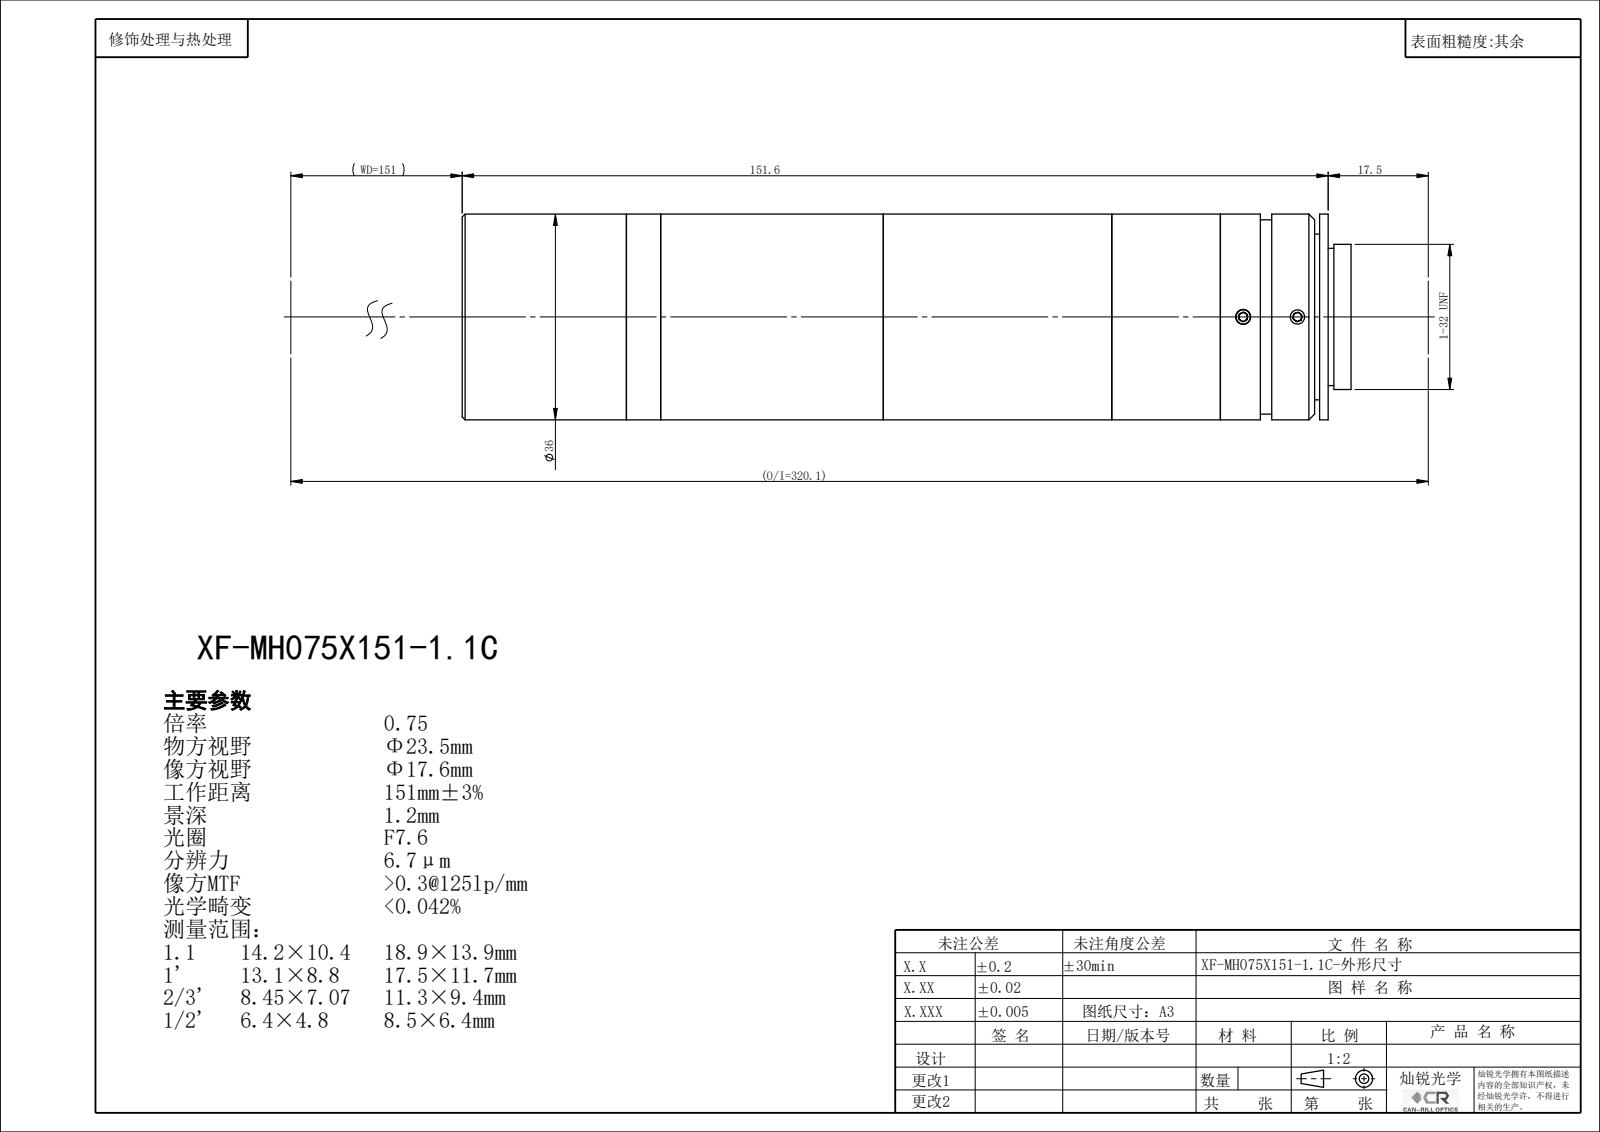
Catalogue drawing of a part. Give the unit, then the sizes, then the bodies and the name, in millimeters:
Units: millimetres
Overall size (bounding box): 155.6 × 36 × 36
Round holes (diameter × count): ⌀2.5 ×3, ⌀22.4 ×1, ⌀24 ×1, ⌀26 ×1, ⌀26.4 ×1, ⌀29.4 ×1, ⌀33.4 ×1, ⌀34.5 ×1
Round bosses / shafts (diameter × count): ⌀36 ×1, ⌀34 ×1, ⌀25.4 ×1
Main face-to-face distances: 18.88, 1.5, 17.38, 19, 36.38, 37.88, 40, 59, 76.38, 77.88
Bodies: 0 solids, 132 faces (68 planar, 42 cylindrical, 22 other)
Part name (STEP PRODUCT): XF-MH075X151-1.1C
STEP written by: SolidWorks 2022 (CONFIG_CONTROL_DESIGN)
